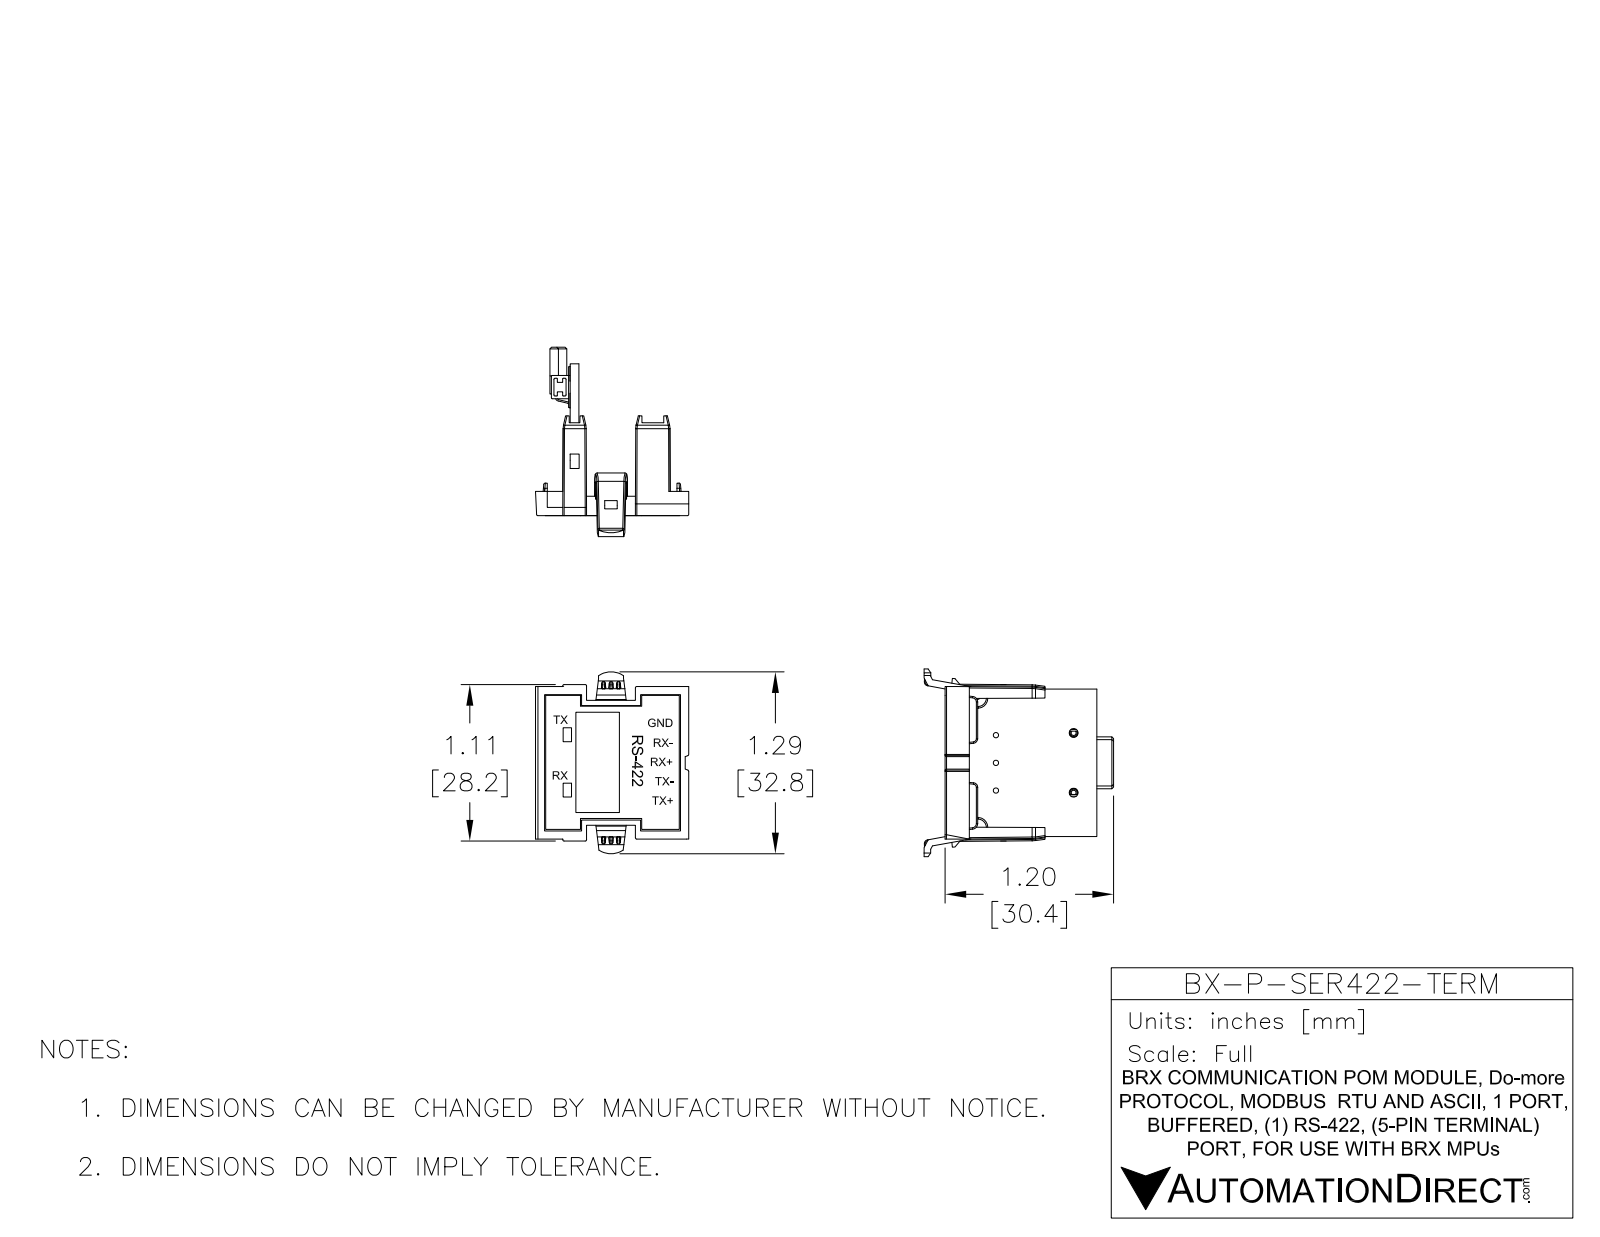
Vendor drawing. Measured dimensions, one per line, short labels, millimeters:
name: BX-P-SER422-TERM
written by: SolidWorks 2017 (AUTOMOTIVE_DESIGN)
unit: mm
bodies: 35 solids, 1912 faces (1437 planar, 318 cylindrical, 157 other)
size: 41 × 33.9 × 27.5
volume: 6 180 mm³; area: 10 300 mm²
holes: 5× ⌀0.3, 5× ⌀1, 5× ⌀2, 5× ⌀2.8, 3× ⌀0.9, 2× ⌀1.6
bosses: 5× ⌀2.6, 5× ⌀0.3
rounds: 56× R0.1, 27× R0.2, 10× R0.3, 10× R0.4, 8× R0.3, 5× R1.2, 5× R1.8, 5× R1.8
face distances: 7, 1.6, 3.5, 0.5, 3, 3.5, 8.4, 10.5, 8.6, 12
hole spacings: 3.5, 7, 14.5, 10.5, 14, 14, 14, 15.7
